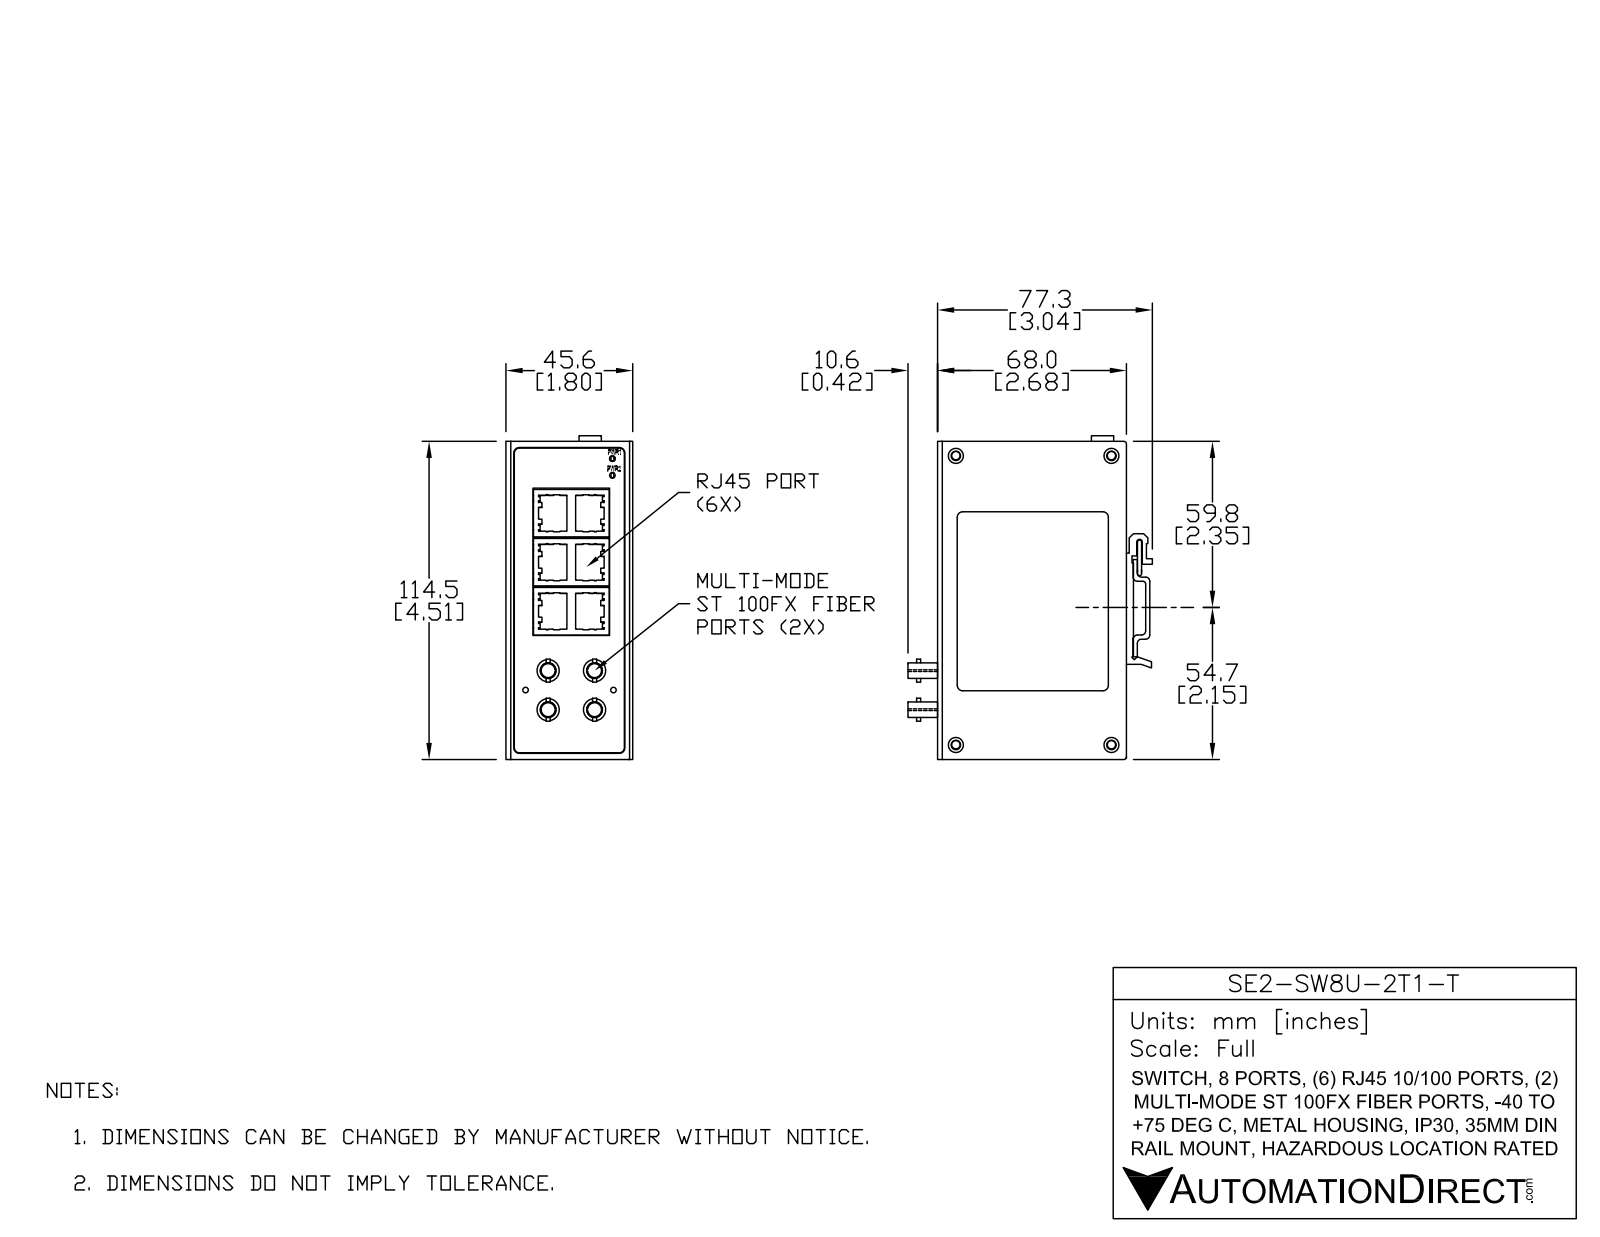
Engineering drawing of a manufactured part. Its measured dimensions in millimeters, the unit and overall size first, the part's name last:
Units: millimetres
Overall size (bounding box): 114.5 × 87.5 × 45.6
Round holes (diameter × count): ⌀5 ×4, ⌀5.6 ×1
Round bosses / shafts (diameter × count): ⌀8 ×4, ⌀5.6 ×3, ⌀1.4 ×2
Partial cylindrical surfaces — rounded edges, fillets, slot ends (radius × count): R1 ×5
Main face-to-face distances: 45.6, 67.6, 114.5, 2.5, 70.1, 70.5, 68, 0.4, 60.41, 57.91
Hole centre spacings: 14.05, 16.7, 21.82
Volume: 353 743 mm³ · Surface area: 40 204 mm²
Bodies: 3 solids, 426 faces (370 planar, 26 cylindrical, 30 other)
Part name (STEP PRODUCT): SE2-SW8U-2T1-T
STEP written by: SolidWorks 2017 (AUTOMOTIVE_DESIGN)
